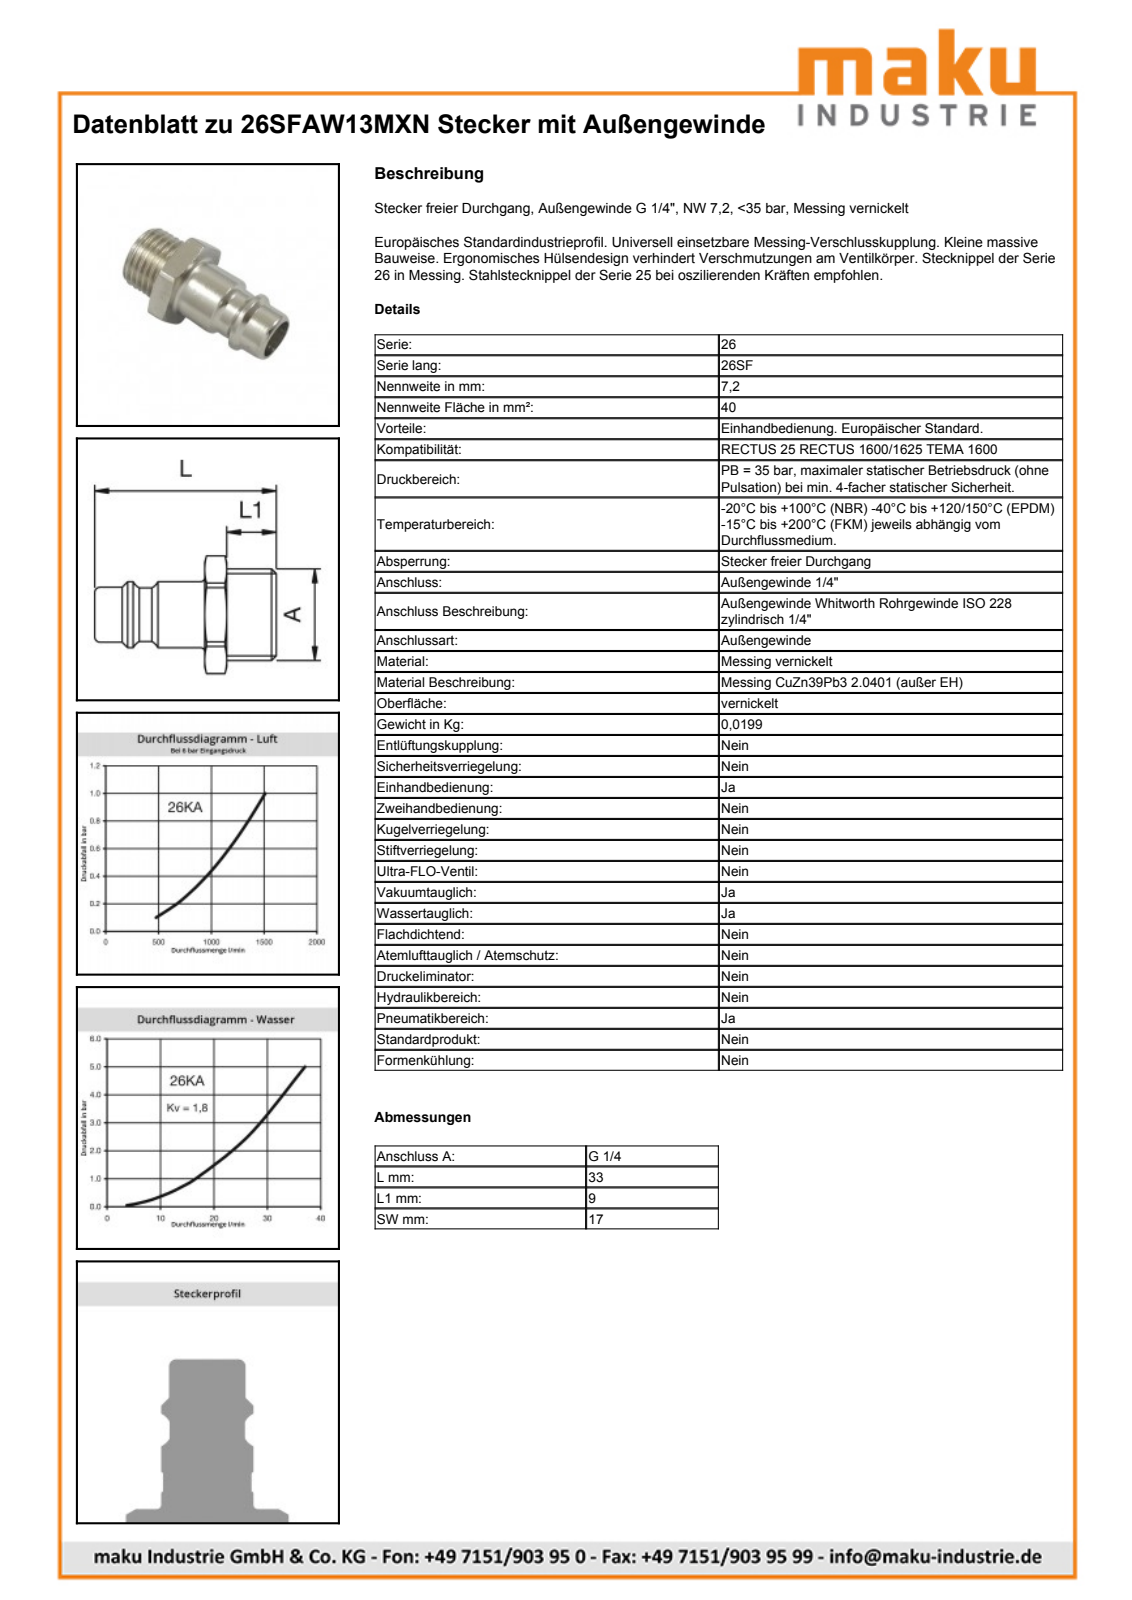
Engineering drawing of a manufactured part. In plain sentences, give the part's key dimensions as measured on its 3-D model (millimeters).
The part is named "D104123". Its 3-D file was written by "Autodesk Inventor 2011 (AUTOMOTIVE_DESIGN)". It is 1 solid with 41 faces: 10 planar, 12 cylindrical and 19 other. Overall it measures 33.1 by 19.15 by 17 millimeters. Its volume is 2 531 cubic millimeters and its surface area 2 464 square millimeters. Round holes: 1 of diameter 7.85. Round bosses or shafts: 1 of diameter 13.16, 1 of diameter 12, 1 of diameter 10, 1 of diameter 9.75. Partial cylindrical surfaces (rounded edges, fillets, slot ends): 1 of radius 9.57. The main face-to-face distances are 17, 4.1, 13.1, 9, 20, 24.1, 33.1.
